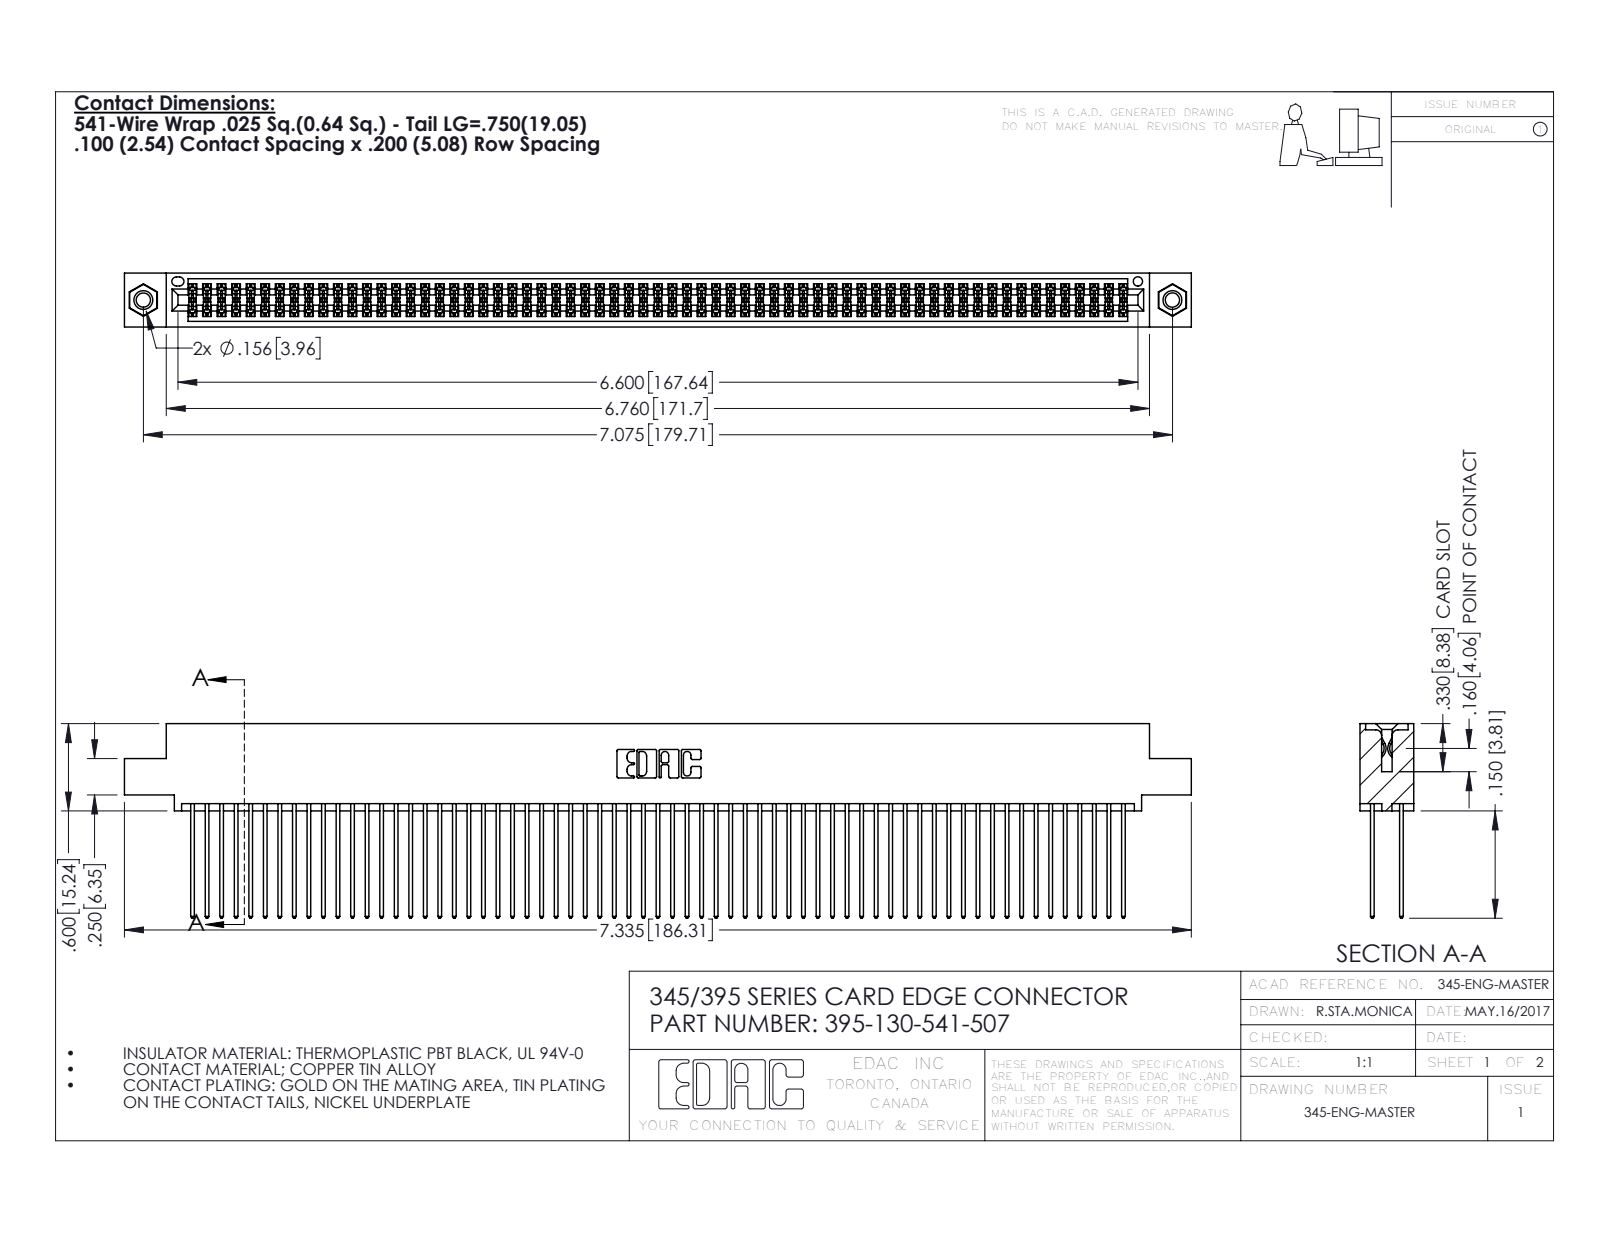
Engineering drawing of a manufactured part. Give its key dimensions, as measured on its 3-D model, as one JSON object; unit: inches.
{"part_name": "345-292-001_345-293-141; 345 Part_0.110 Offset - 0.156 Dia-TI; 345-250-001_345-250-005-103; 395-130-541-507", "step_written_by": "SolidWorks 2016 (CONFIG_CONTROL_DESIGN)", "units": "inches", "bodies": {"solids": 133, "faces": 6690, "planar": 4406, "cylindrical": 2268, "other": 16}, "overall_size": [7.335, 1.337, 0.37], "volume_in3": 1.158, "surface_area_in2": 49.78, "round_holes": [[0.098, 2], [0.125, 2], [0.156, 2], [0.064, 1]], "round_bosses_or_shafts": [[0.155, 2]], "partial_cylinders_radius": [[0.006, 195], [0.01, 130], [0.01, 22], [0.007, 6], [0.031, 6], [0.026, 3], [0.014, 2], [0.019, 2]], "face_to_face_distances": [0.072, 0.298, 0.2, 0.098, 0.272, 0.025, 0.225, 0.37, 0.175, 0.149], "hole_center_spacings": [0.27, 6.839, 7.075]}
